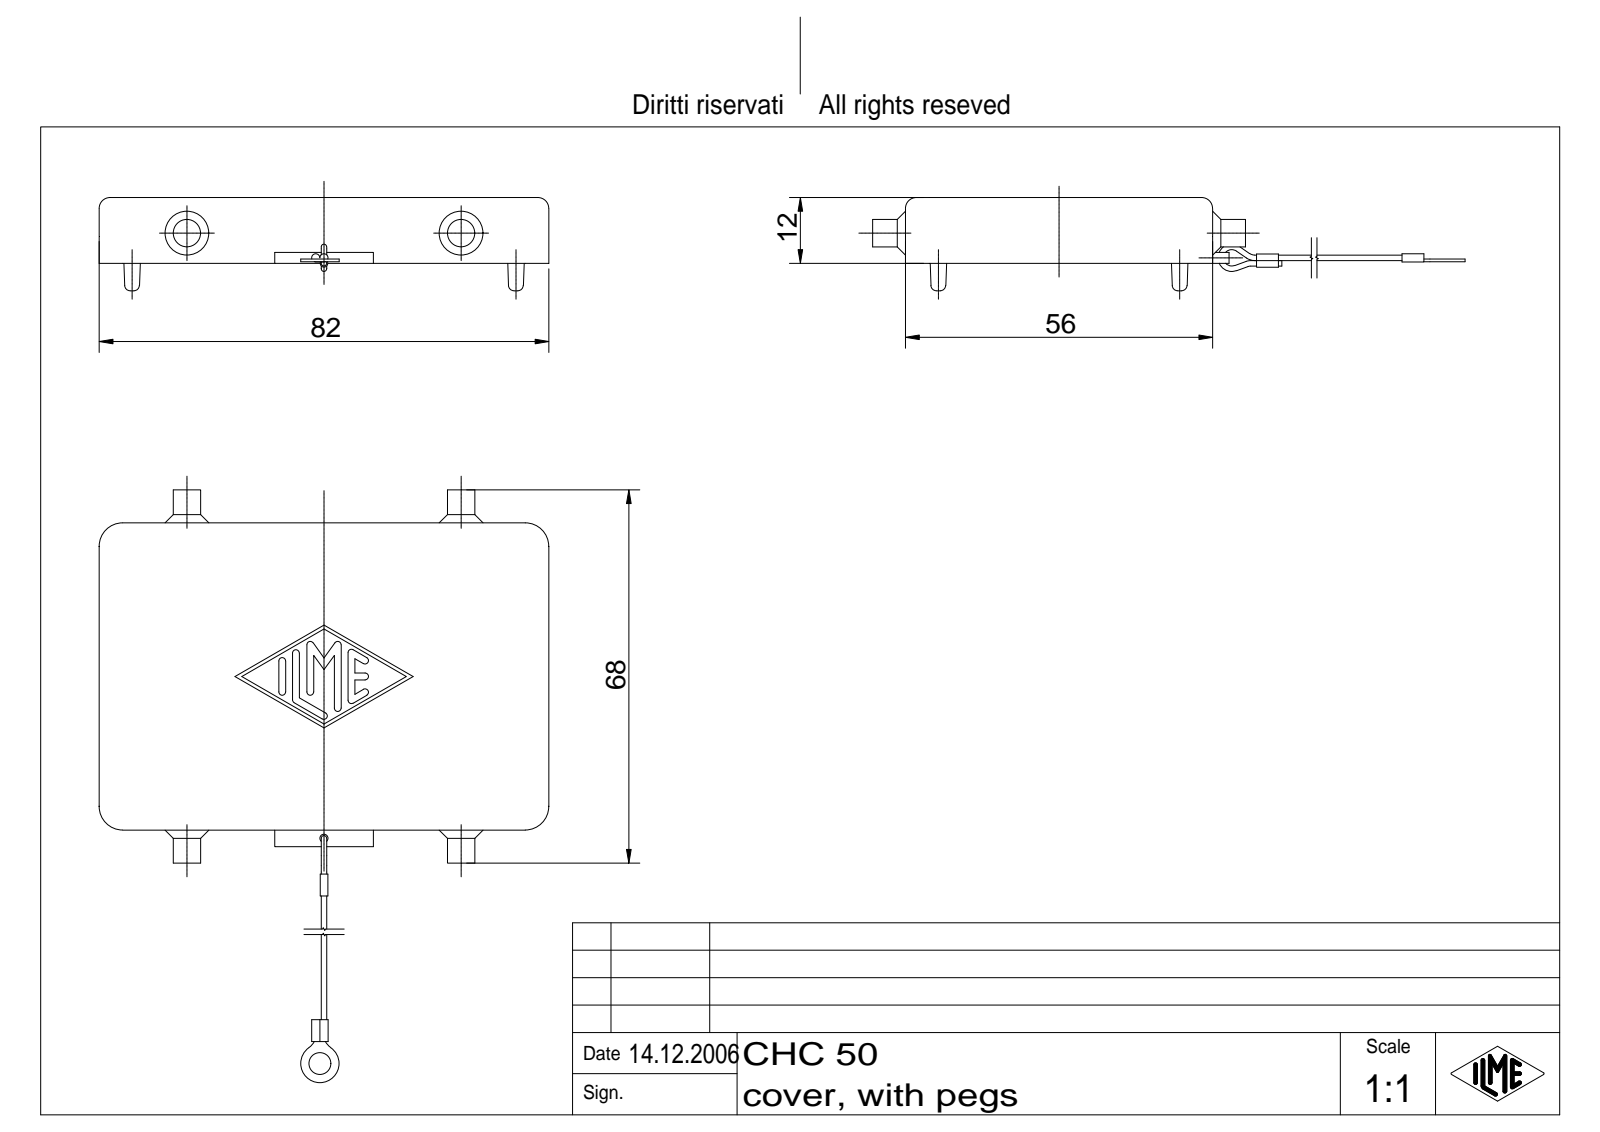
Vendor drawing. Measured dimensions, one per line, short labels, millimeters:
name: CHC 50
written by: Autodesk Inventor 7 (AUTOMOTIVE_DESIGN)
unit: mm
bodies: 1 solid, 182 faces (70 planar, 64 cylindrical, 48 other)
size: 173 × 82 × 17
volume: 22 507 mm³; area: 15 398 mm²
holes: 1× ⌀1.5, 1× ⌀4
bosses: 4× ⌀1, 2× ⌀5, 1× ⌀7
rounds: 14× R0.62, 4× R2, 4× R4.3, 2× R0.7, 2× R0.75, 2× R3
face distances: 3, 53, 9, 12, 56, 79, 50, 82, 76, 77.78
hole spacings: 106
